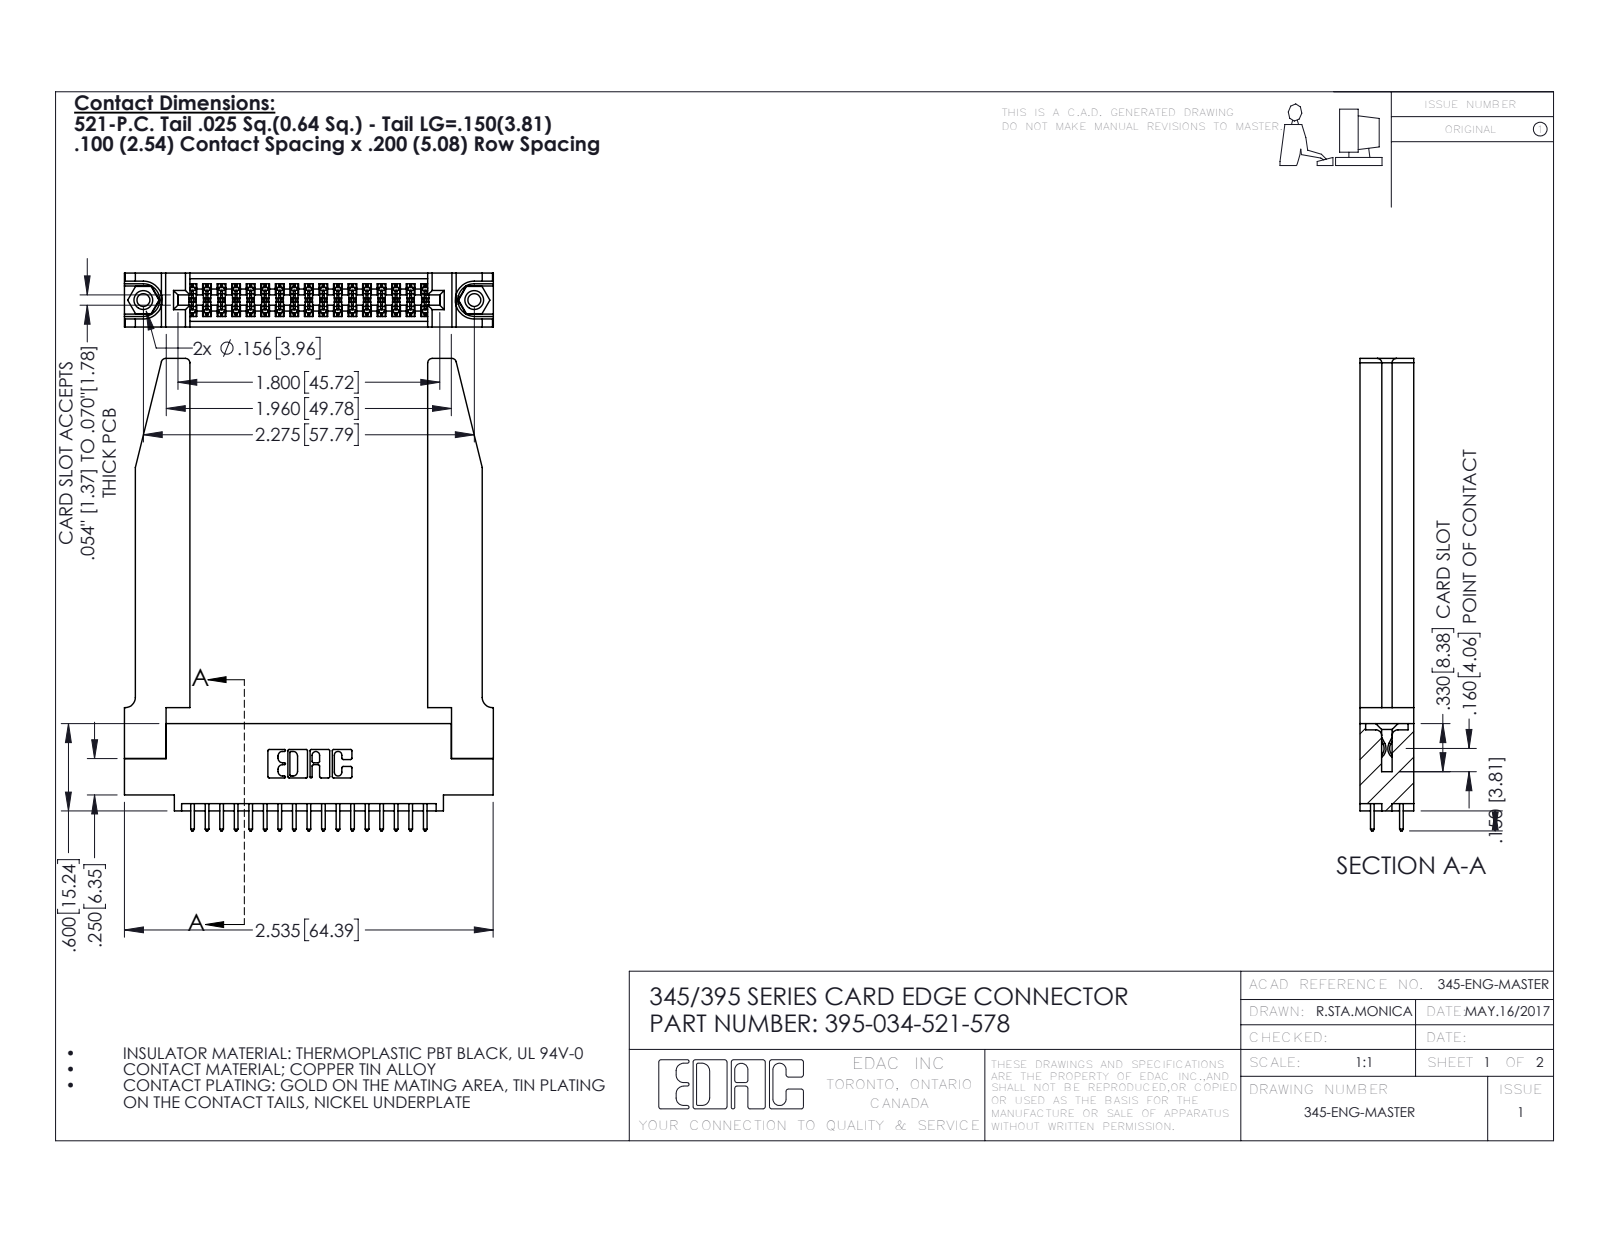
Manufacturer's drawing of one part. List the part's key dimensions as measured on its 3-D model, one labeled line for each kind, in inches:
Part name (STEP PRODUCT): 345-250-001_345-250-001-102; 345-220-078_345-220-078; 345 Part_0.110 Offset - 0.156 Dia-TH; 345-292-001_345-293-121 (+1 more)
STEP written by: SolidWorks 2016 (CONFIG_CONTROL_DESIGN)
Units: inches
Bodies: 39 solids, 2064 faces (1348 planar, 664 cylindrical, 52 other)
Overall size (bounding box): 3.247 × 2.536 × 0.37
Volume: 0.837 in³ · Surface area: 23.46 in²
Round holes (diameter × count): ⌀0.089 ×2, ⌀0.125 ×2, ⌀0.156 ×2, ⌀0.064 ×1
Round bosses / shafts (diameter × count): ⌀0.155 ×2
Partial cylindrical surfaces — rounded edges, fillets, slot ends (radius × count): R0.006 ×51, R0.01 ×34, R0.01 ×22, R0.03 ×8, R0.007 ×6, R0.031 ×6, R0.026 ×3, R0.014 ×2
Main face-to-face distances: 0.37, 0.072, 0.298, 0.2, 0.098, 0.272, 0.025, 0.148, 0.15, 0.225
Hole centre spacings: 0.27, 2.041, 2.275
